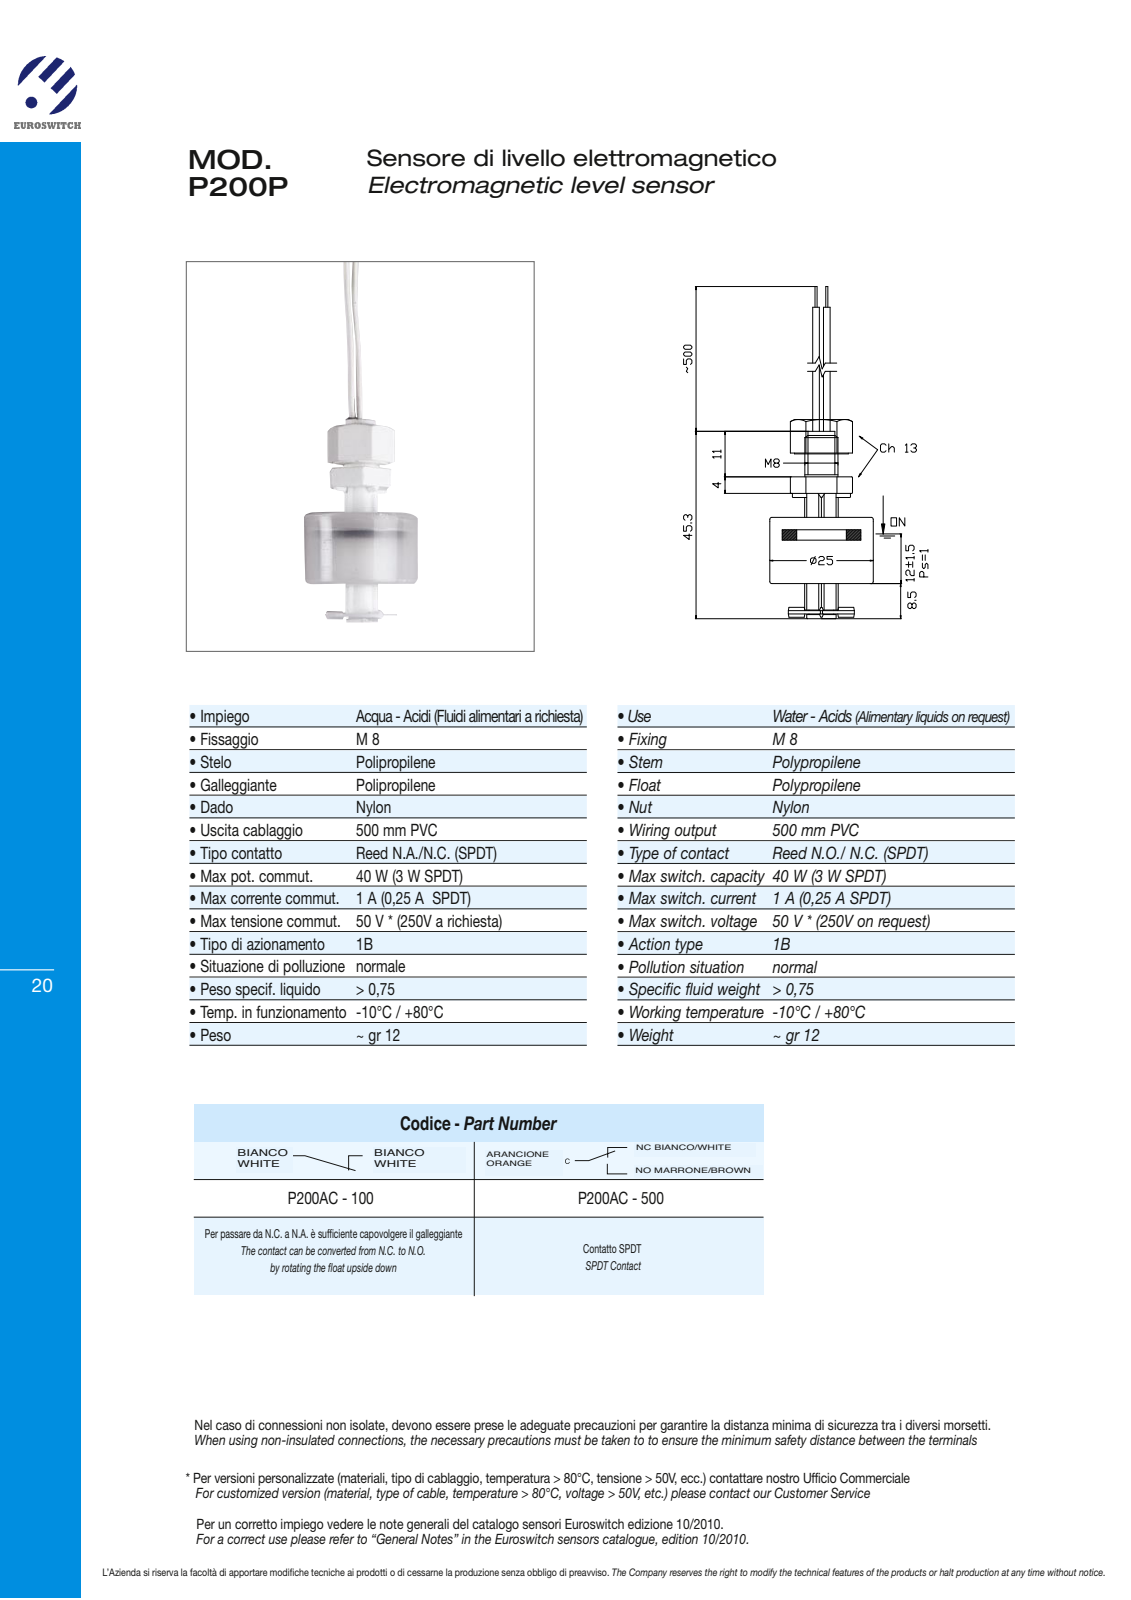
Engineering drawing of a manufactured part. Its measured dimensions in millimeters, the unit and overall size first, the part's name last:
Units: millimetres
Overall size (bounding box): 263.3 × 25 × 25
Round holes (diameter × count): ⌀9.8 ×1, ⌀9.9 ×1
Round bosses / shafts (diameter × count): ⌀1.3 ×2, ⌀0.5 ×2, ⌀25 ×1, ⌀16 ×1, ⌀13 ×1, ⌀7.1 ×1, ⌀6.5 ×1
Partial cylindrical surfaces — rounded edges, fillets, slot ends (radius × count): R0.2 ×26, R0.25 ×3
Main face-to-face distances: 16.2, 13, 4, 21.1, 28.2, 20.2, 0.9, 4.9, 1.2, 24.2
Bodies: 0 solids, 163 faces (64 planar, 66 cylindrical, 33 other)
Part name (STEP PRODUCT): P200AC-100
STEP written by: SolidWorks 2019 (AUTOMOTIVE_DESIGN)
